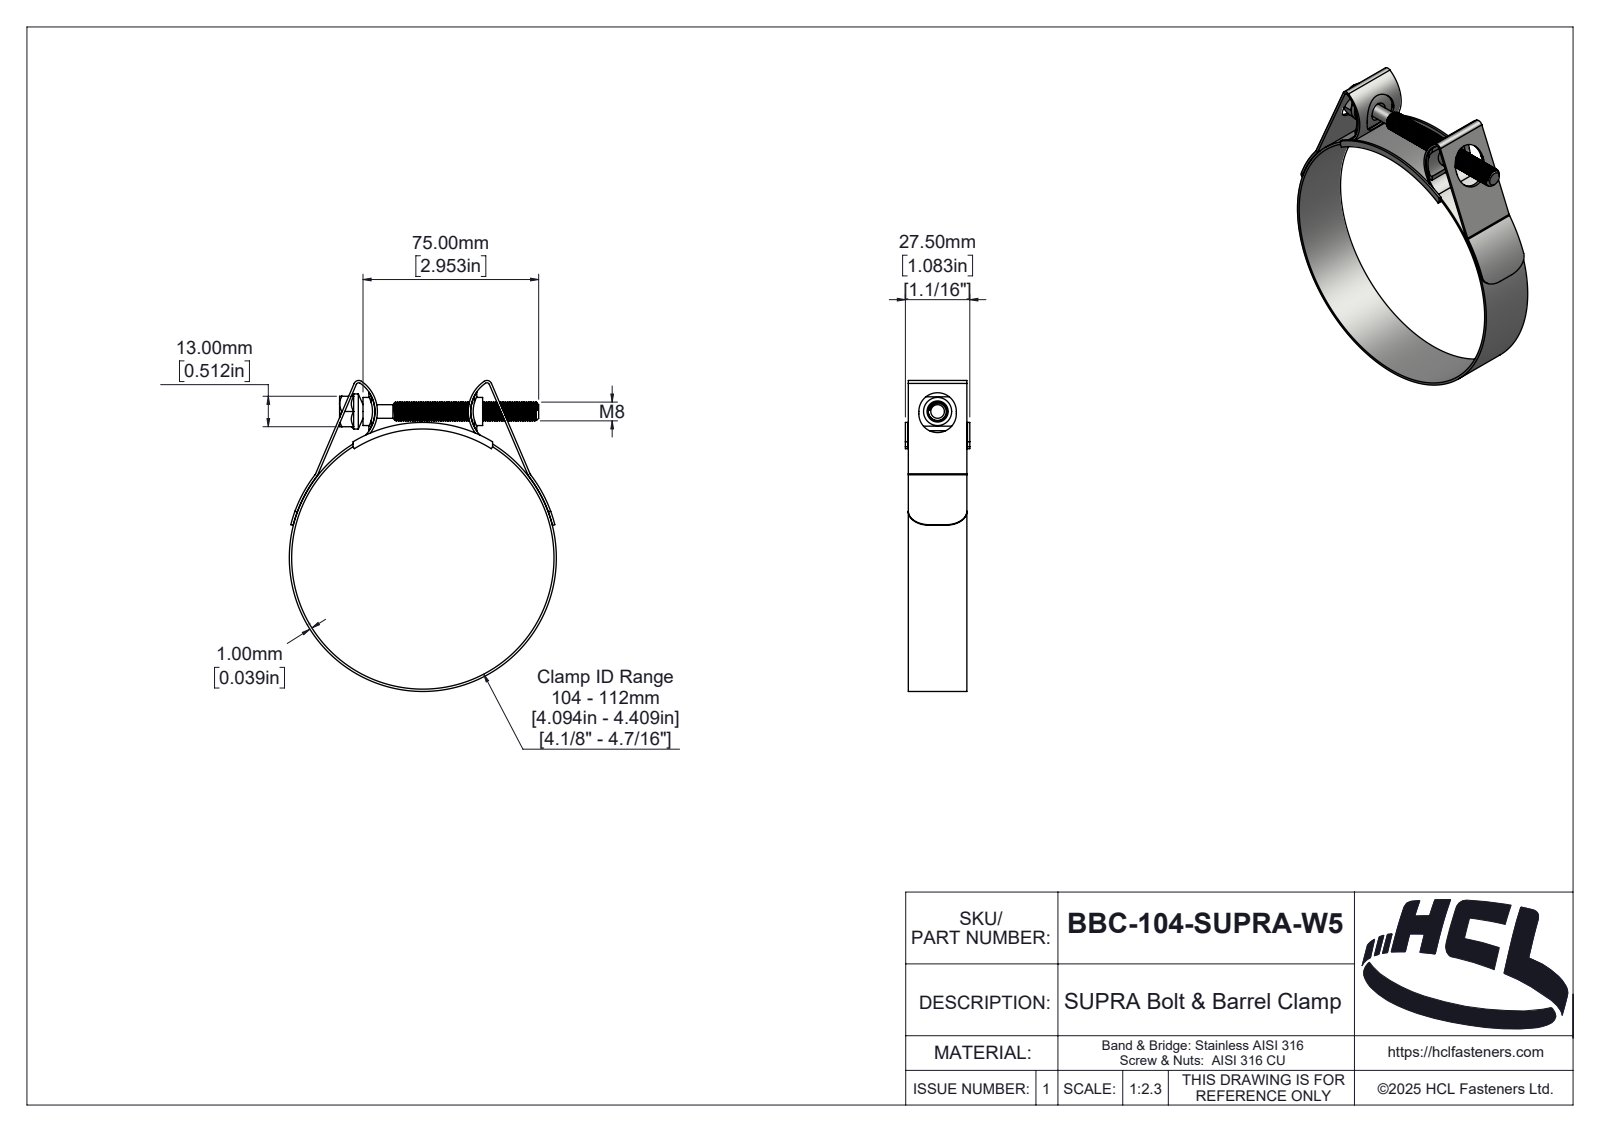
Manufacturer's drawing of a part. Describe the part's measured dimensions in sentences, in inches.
The part is named "BBC-104-SUPRA-W5". Its 3-D file was written by "SolidWorks 2025 (AUTOMOTIVE_DESIGN)". It is 5 solids with 365 faces: 46 planar, 233 cylindrical and 86 other. Overall it measures 5.225 by 4.488 by 1.083 inches. Its volume is 1.158 cubic inches and its surface area 51.96 square inches. Round holes: 1 of diameter 4.409. Round bosses or shafts: 1 of diameter 4.488, 1 of diameter 0.591, 1 of diameter 0.472, 1 of diameter 0.315, 1 of diameter 0.228. Partial cylindrical surfaces (rounded edges, fillets, slot ends): 4 of radius 0.039, 2 of radius 0.043, 2 of radius 0.079, 2 of radius 0.083, 2 of radius 0.118, 2 of radius 0.315, 2 of radius 0.532, 2 of radius 0.571. The main face-to-face distances are 0.039, 0.984, 0.049, 1.033, 1.043, 0.994, 1.083, 1.004, 0.512, 0.098.
